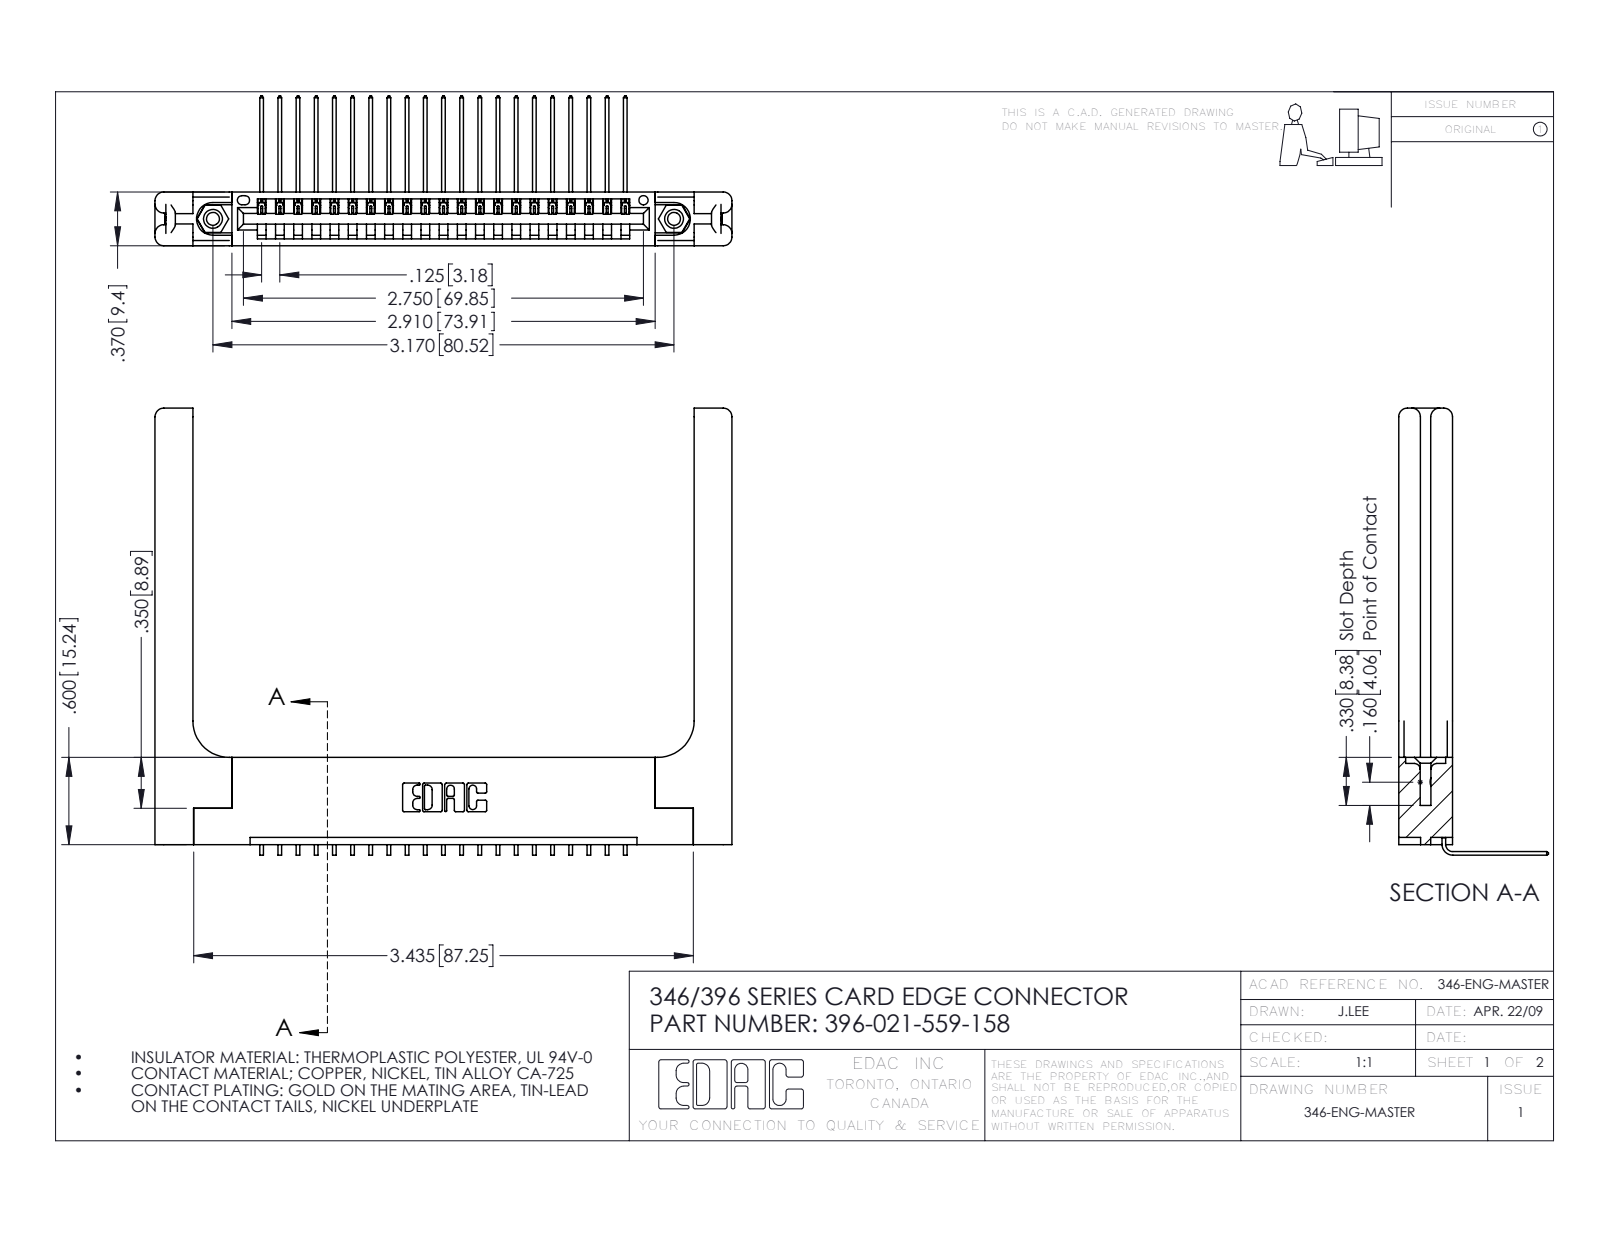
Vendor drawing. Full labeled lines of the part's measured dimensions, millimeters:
Part name (STEP PRODUCT): 346-220-058_345-220-058; 396-021-559-158; 345-292-001_558 559 Tail - 1; 345-250-001_345-250-001-102 (+1 more)
STEP written by: SolidWorks 2016 (CONFIG_CONTROL_DESIGN)
Units: millimetres
Bodies: 26 solids, 1638 faces (1106 planar, 472 cylindrical, 60 other)
Overall size (bounding box): 100.7 × 78.1 × 26.2
Volume: 17 090 mm³ · Surface area: 17 320 mm²
Round holes (diameter × count): ⌀2.3 ×2, ⌀3.2 ×2, ⌀4 ×2, ⌀1.6 ×1
Round bosses / shafts (diameter × count): ⌀3.9 ×2
Partial cylindrical surfaces — rounded edges, fillets, slot ends (radius × count): R0.2 ×42, R0.3 ×22, R1.5 ×16, R0.2 ×6, R0.8 ×6, R0.7 ×3, R0.8 ×2, R0.8 ×2
Main face-to-face distances: 9.4, 1.8, 1.2, 8.2, 3.8, 3.8, 6.4, 0.6, 7.6, 2.6
Hole centre spacings: 6.2, 75.3, 80.5
